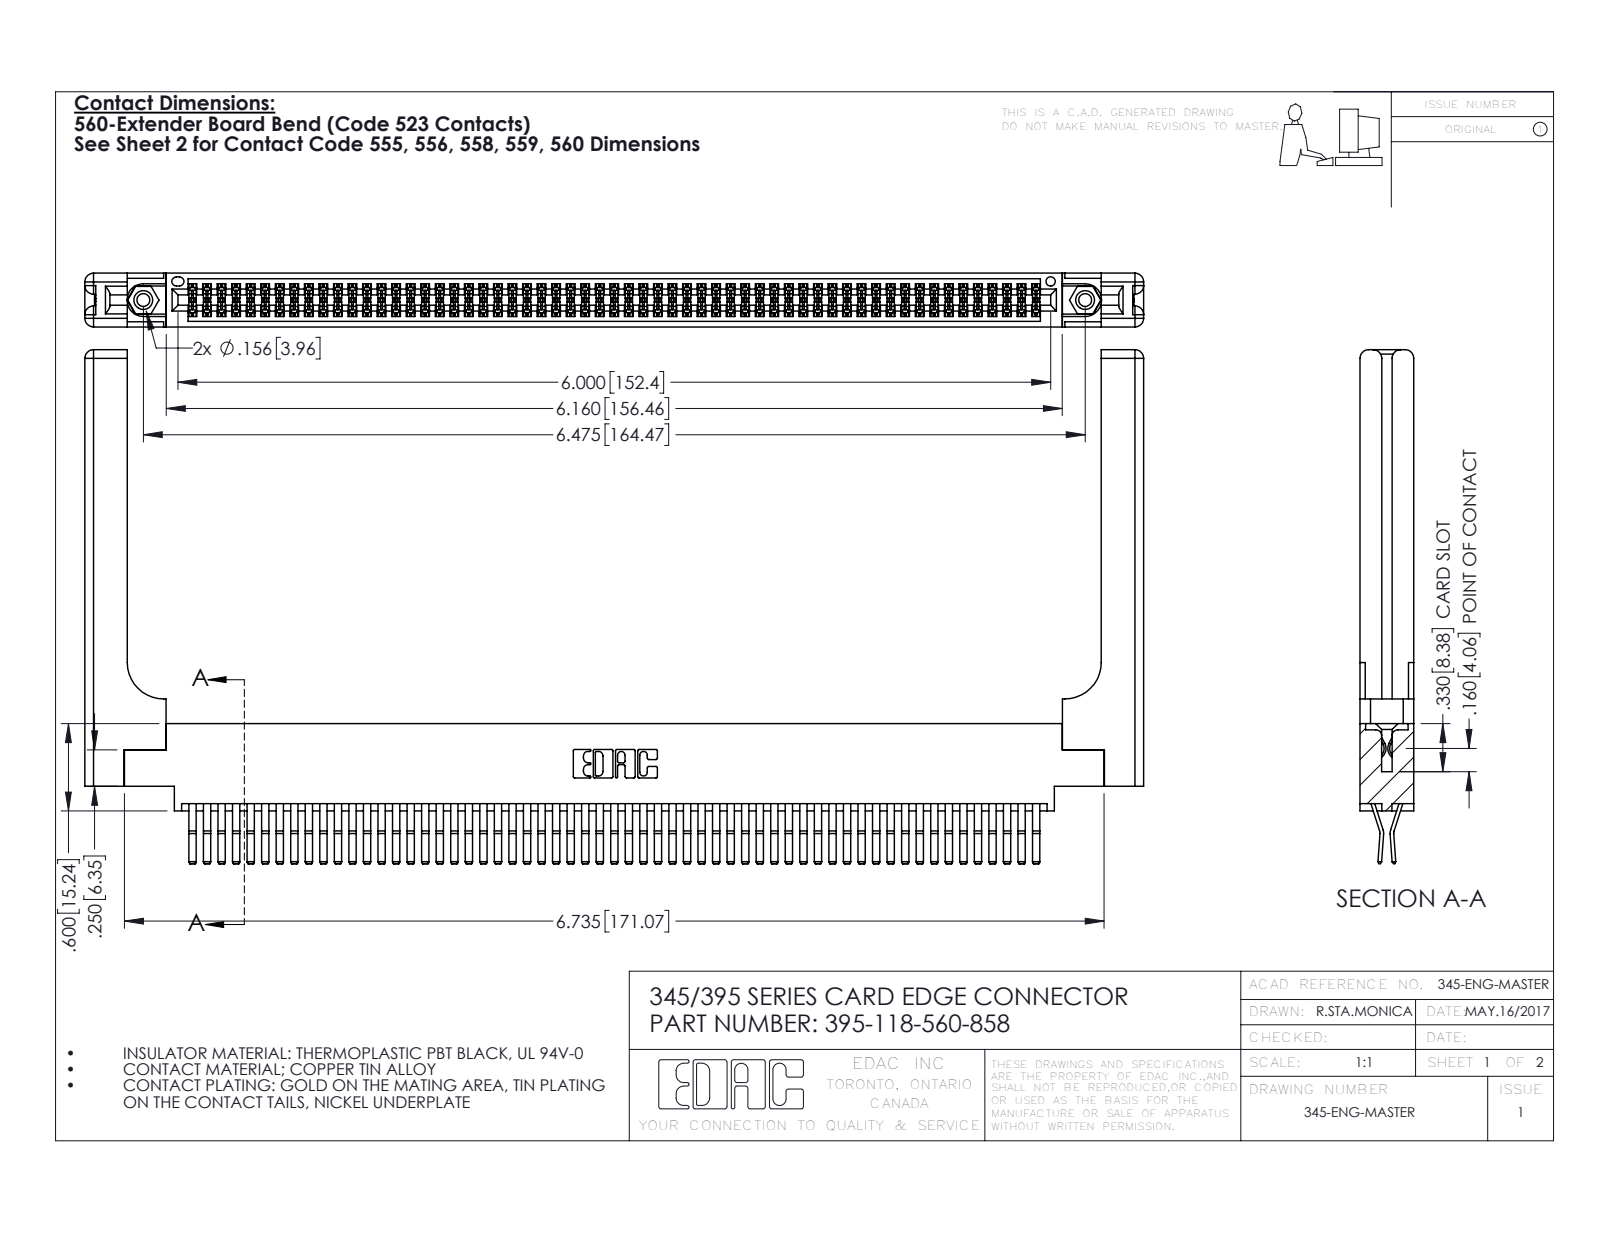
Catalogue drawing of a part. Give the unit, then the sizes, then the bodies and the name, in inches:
Units: inches
Overall size (bounding box): 7.279 × 3.532 × 0.37
Round holes (diameter × count): ⌀0.089 ×2, ⌀0.125 ×2, ⌀0.156 ×2, ⌀0.064 ×1
Round bosses / shafts (diameter × count): ⌀0.155 ×2
Partial cylindrical surfaces — rounded edges, fillets, slot ends (radius × count): R0.006 ×177, R0.01 ×22, R0.06 ×16, R0.007 ×6, R0.031 ×6, R0.026 ×3, R0.01 ×2, R0.014 ×2
Main face-to-face distances: 0.072, 0.37, 0.298, 0.025, 0.098, 0.272, 0.2, 0.225, 0.175, 0.148
Hole centre spacings: 0.27, 6.239, 6.475
Volume: 1.663 in³ · Surface area: 54.68 in²
Bodies: 123 solids, 6522 faces (4126 planar, 2336 cylindrical, 60 other)
Part name (STEP PRODUCT): 345-292-001_560 Tail; 345-250-001_345-250-001-102; 345-220-058_345-220-058; 395-118-560-858 (+1 more)
STEP written by: SolidWorks 2016 (CONFIG_CONTROL_DESIGN)
